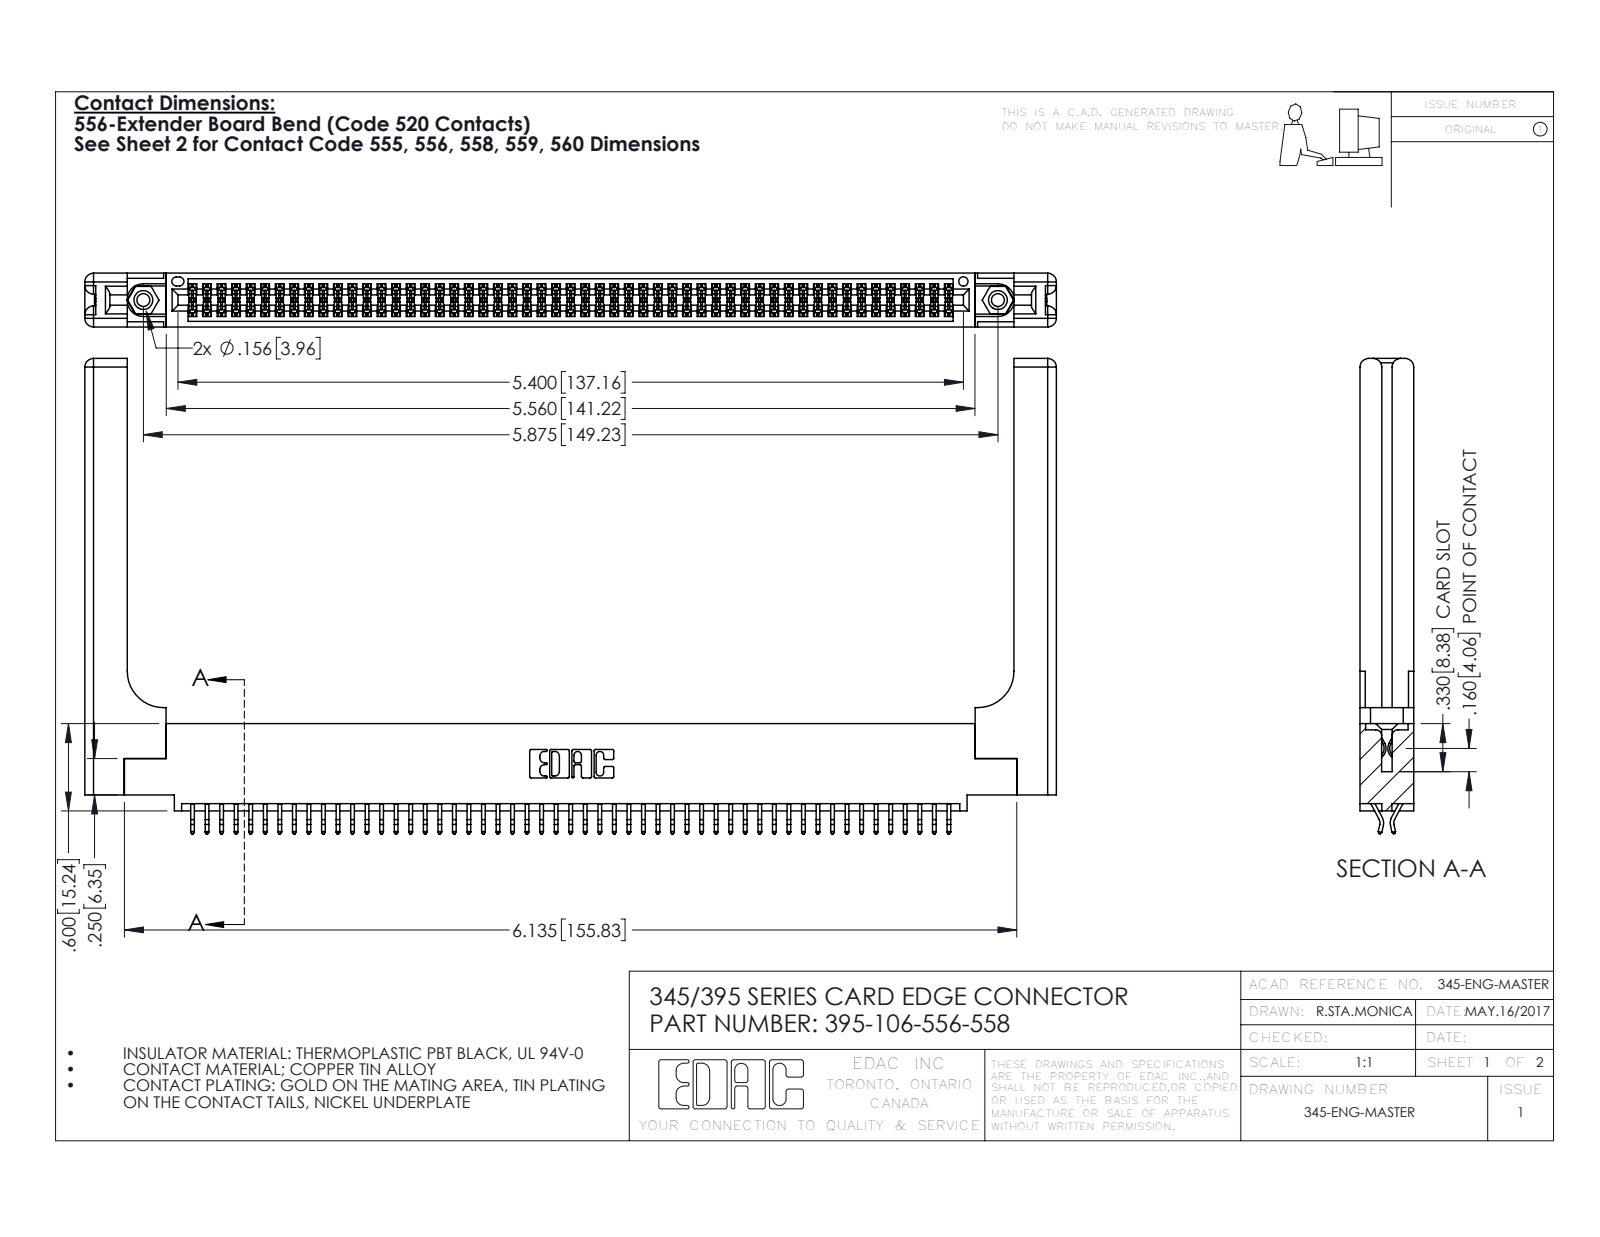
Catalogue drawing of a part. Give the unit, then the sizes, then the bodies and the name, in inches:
Units: inches
Overall size (bounding box): 6.679 × 3.267 × 0.37
Round holes (diameter × count): ⌀0.089 ×2, ⌀0.125 ×2, ⌀0.156 ×2, ⌀0.064 ×1
Round bosses / shafts (diameter × count): ⌀0.155 ×2
Partial cylindrical surfaces — rounded edges, fillets, slot ends (radius × count): R0.006 ×159, R0.01 ×22, R0.06 ×16, R0.007 ×6, R0.031 ×6, R0.026 ×3, R0.01 ×2, R0.014 ×2
Main face-to-face distances: 0.072, 0.298, 0.37, 0.025, 0.098, 0.272, 0.2, 0.225, 0.148, 0.15
Hole centre spacings: 0.27, 5.639, 5.875
Volume: 1.524 in³ · Surface area: 45.99 in²
Bodies: 111 solids, 6322 faces (4154 planar, 2108 cylindrical, 60 other)
Part name (STEP PRODUCT): 345-292-001_556 Tail; 395-106-556-558; 345-220-058_345-220-058; 345 Part_0.110 Offset - 0.156 Dia-TH (+1 more)
STEP written by: SolidWorks 2016 (CONFIG_CONTROL_DESIGN)
